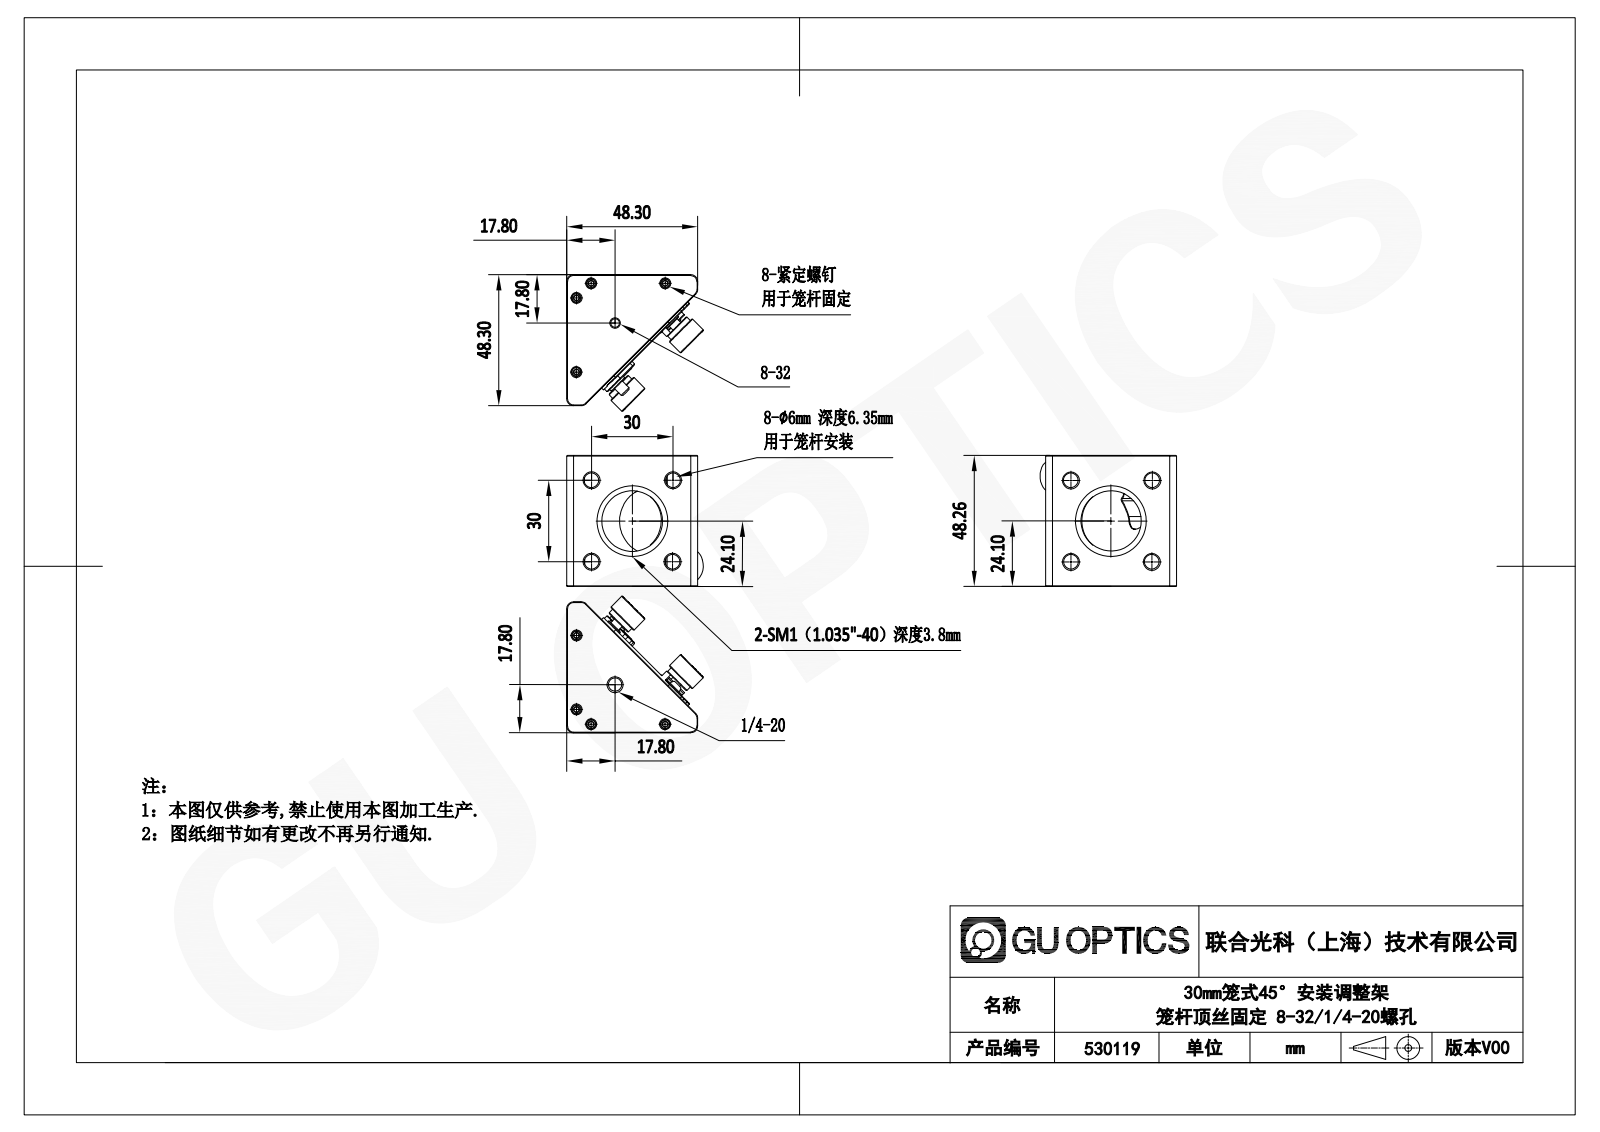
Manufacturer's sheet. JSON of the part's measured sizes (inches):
{"part_name": "530119", "step_written_by": "SolidWorks 2020 (CONFIG_CONTROL_DESIGN)", "units": "inches", "bodies": {"solids": 41, "faces": 720, "planar": 366, "cylindrical": 191, "other": 163}, "overall_size": [2.127, 2.127, 1.9], "volume_in3": 2.914, "surface_area_in2": 43.8, "round_holes": [[0.236, 6], [0.118, 4], [0.13, 4], [0.25, 4], [0.114, 3], [0.138, 3], [0.14, 3], [0.146, 3], [0.148, 3], [0.276, 3], [0.063, 2], [0.094, 2]], "round_bosses_or_shafts": [[0.157, 8], [0.059, 5], [0.472, 3], [0.394, 3], [0.079, 3], [0.268, 2], [0.236, 2], [0.217, 2]], "partial_cylinders_radius": [[0.031, 30], [0.039, 7], [0.037, 6], [0.1, 5], [0.031, 4], [0.05, 4], [0.17, 4], [0.25, 4]], "face_to_face_distances": [0.045, 1.9, 0.163, 0.118, 0.398, 0.28, 0.235, 0.068, 0.33, 0.212], "hole_center_spacings": [1.181, 0.835, 1.3, 1.453, 1.67, 0.215, 0.991, 1.2]}
